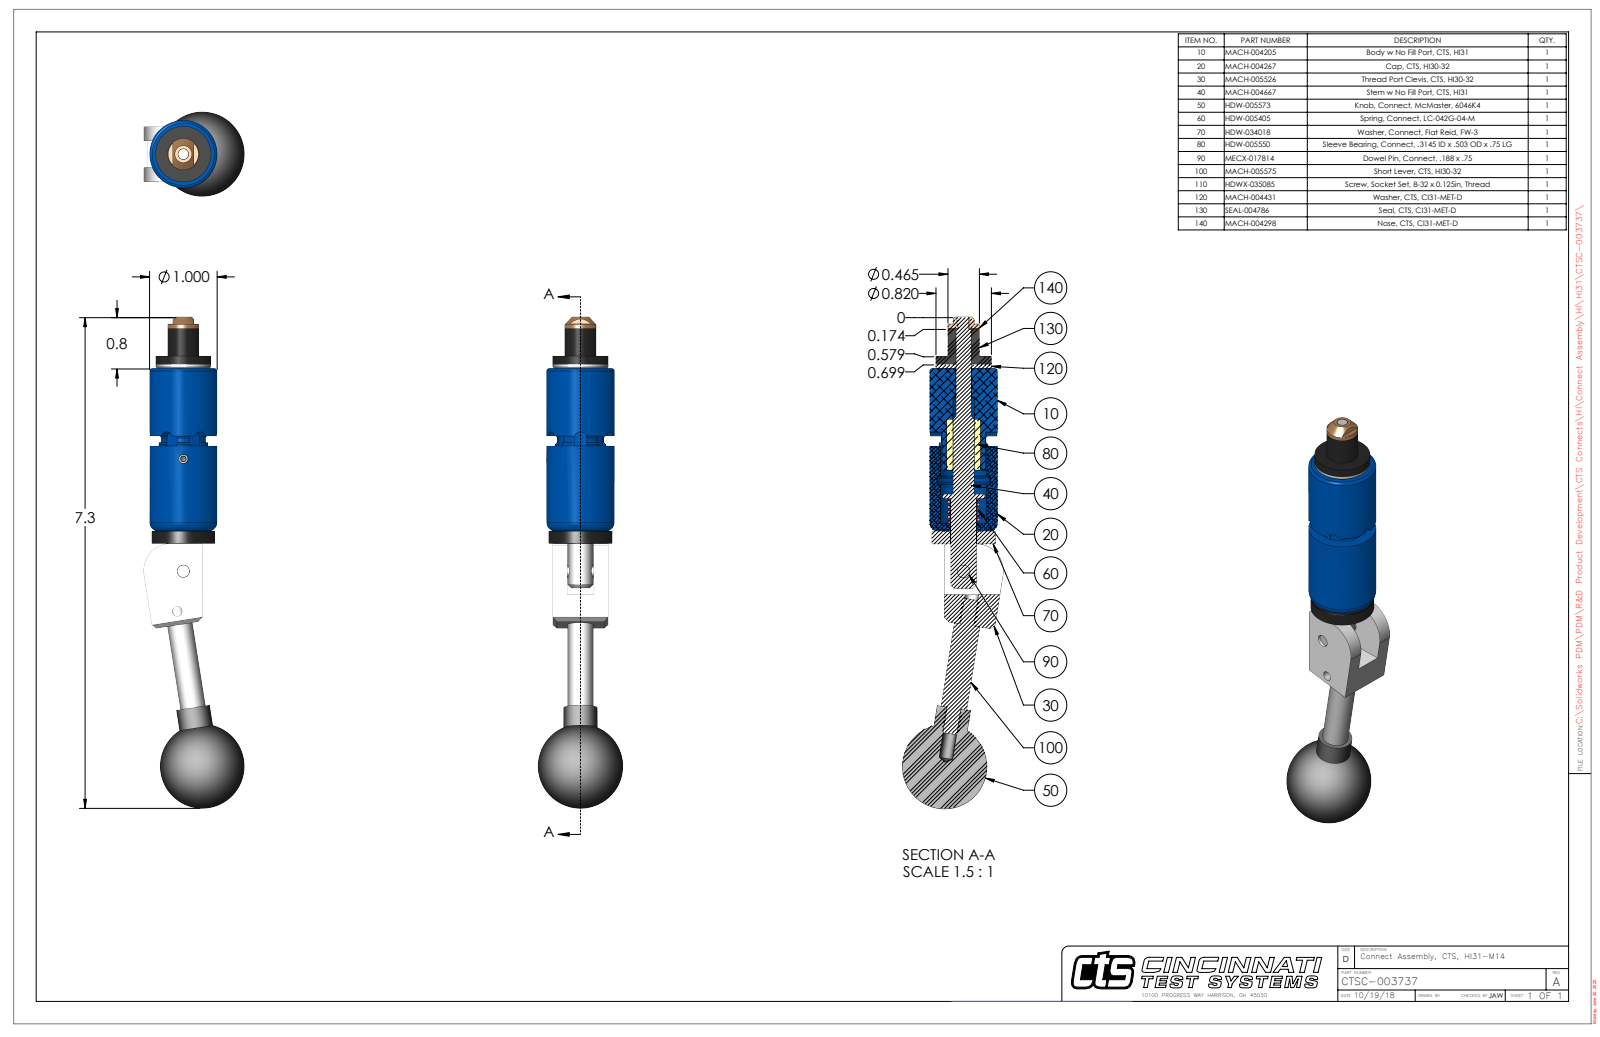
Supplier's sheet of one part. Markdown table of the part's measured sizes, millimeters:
| quantity | value |
| --- | --- |
| part name | CTSC-003737 |
| STEP written by | SolidWorks 2023 (AUTOMOTIVE_DESIGN) |
| units | millimeters |
| bodies | 9 solids, 268 faces (101 planar, 109 cylindrical, 58 other) |
| overall size | 184.3 × 37.9 × 31.8 |
| volume | 64 340 mm³ |
| surface area | 20 990 mm² |
| round holes (diameter × count) | 5.1 × 2, 3.5 × 1, 3.8 × 1, 4 × 1, 4.8 × 1, 5.5 × 1, 5.8 × 1, 5.8 × 1, 9.8 × 1, 10 × 1, 17.5 × 1 |
| round bosses / shafts (diameter × count) | 25.4 × 1, 23.8 × 1, 20.8 × 1, 12.7 × 1, 11.8 × 1, 11.8 × 1, 9.7 × 1, 9.5 × 1 |
| partial cylindrical surfaces (radius × count) | 2.4 × 6, 0.7 × 2, 9.5 × 1, 10.2 × 1, 11.6 × 1 |
| main face-to-face distances | 5.3, 15.3, 1.5, 62.5, 61, 20.6, 67.2, 65.7, 4.7, 9.9 |
| hole center spacings | 15.2, 42.1, 57.2 |
